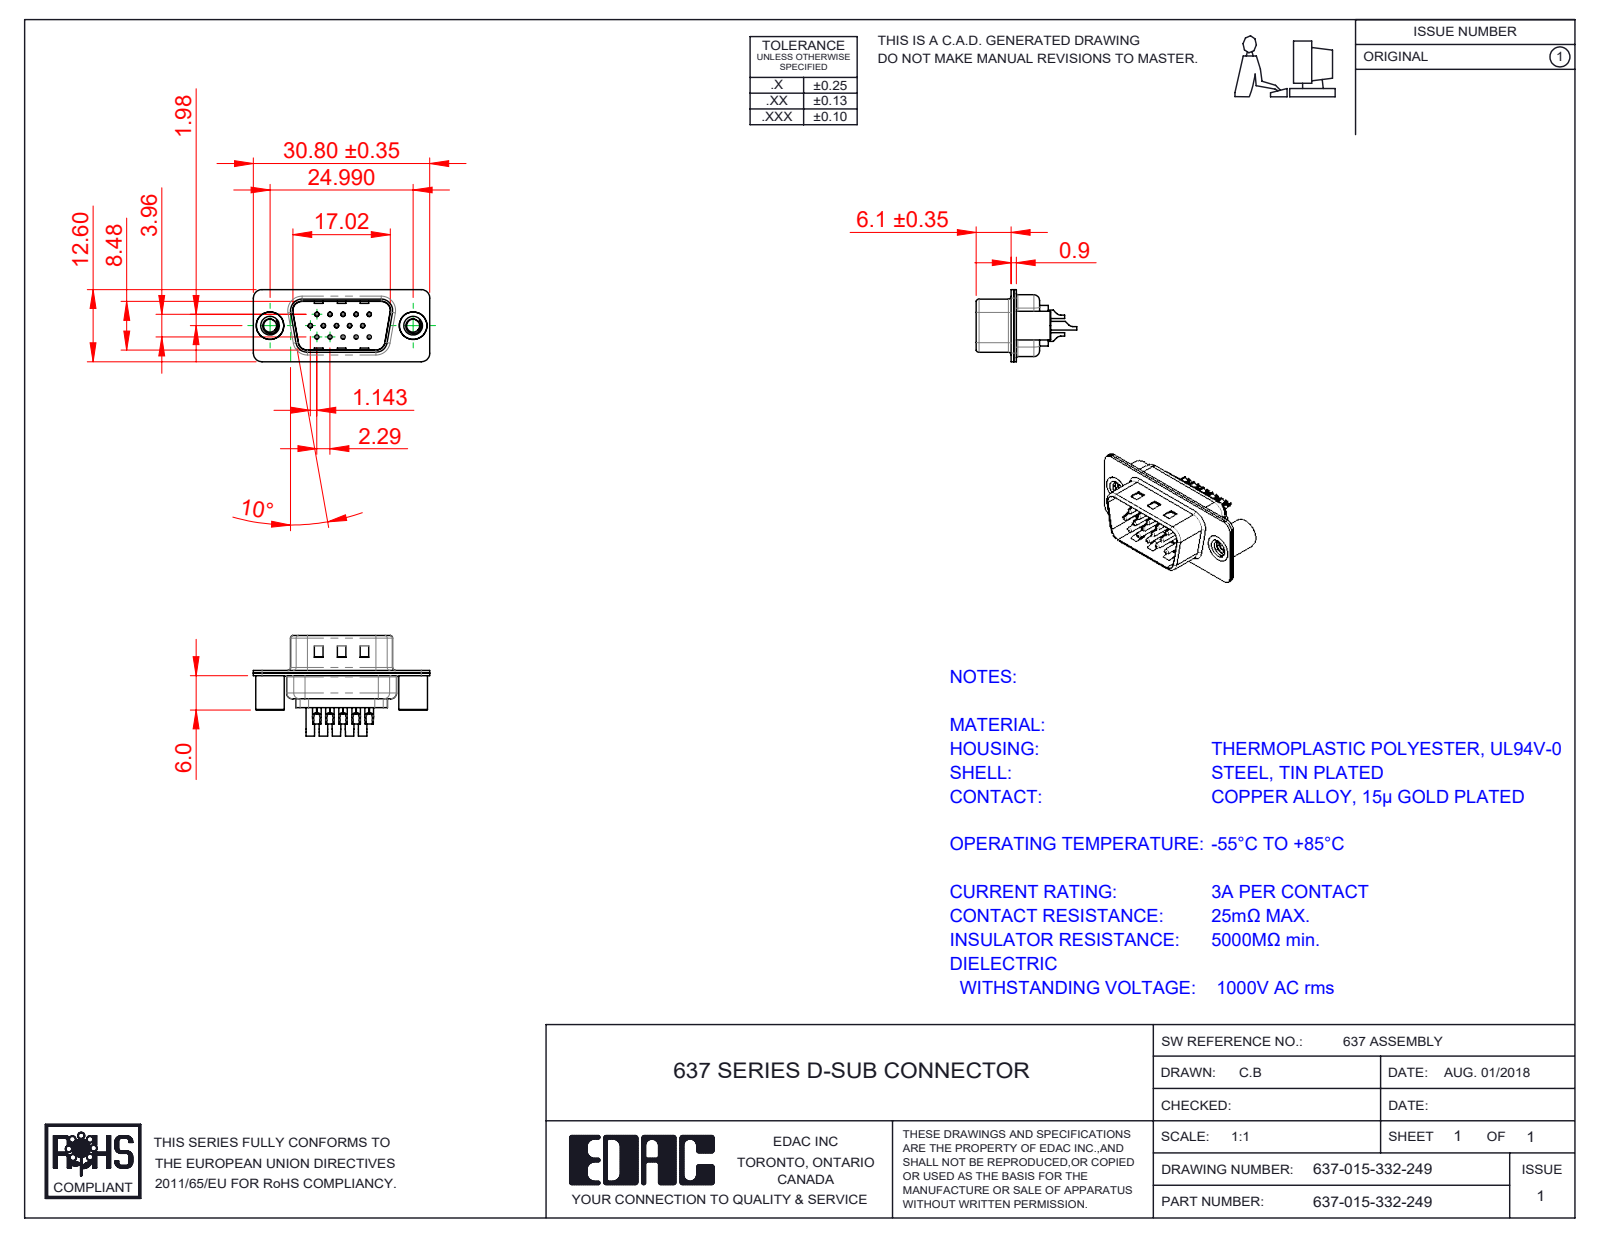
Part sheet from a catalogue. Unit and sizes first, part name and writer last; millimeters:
Units: millimetres
Overall size (bounding box): 30.8 × 17.55 × 12.6
Round holes (diameter × count): ⌀0.35 ×15, ⌀1.1 ×15, ⌀1.6 ×15, ⌀2.26 ×2, ⌀4 ×2, ⌀4.8 ×2
Round bosses / shafts (diameter × count): ⌀2 ×15, ⌀1.5 ×15, ⌀0.75 ×15, ⌀5 ×2, ⌀4.9 ×2, ⌀4.5 ×2
Partial cylindrical surfaces — rounded edges, fillets, slot ends (radius × count): R1.5 ×16, R2 ×12, R0.5 ×8, R1 ×7, R0.25 ×4, R0.55 ×4, R0.7 ×4, R0.95 ×4
Main face-to-face distances: 0.45, 0.9, 0.4, 0.7, 8.88, 8.48, 1.05, 0.31, 4.55, 1.16
Hole centre spacings: 3.96, 2.28, 4.57, 2.29, 6.05, 6.86, 7.92, 6.04
Volume: 1 394 mm³ · Surface area: 4 972 mm²
Bodies: 20 solids, 1298 faces (319 planar, 592 cylindrical, 387 other)
Part name (STEP PRODUCT): 637 Shell Rear_15 Contacts; 637 Shell Front_15 Contacts; 637 Contact Row 2_32; 637 Housing_15 Contacts (+4 more)
STEP written by: SolidWorks 2020 (CONFIG_CONTROL_DESIGN)
